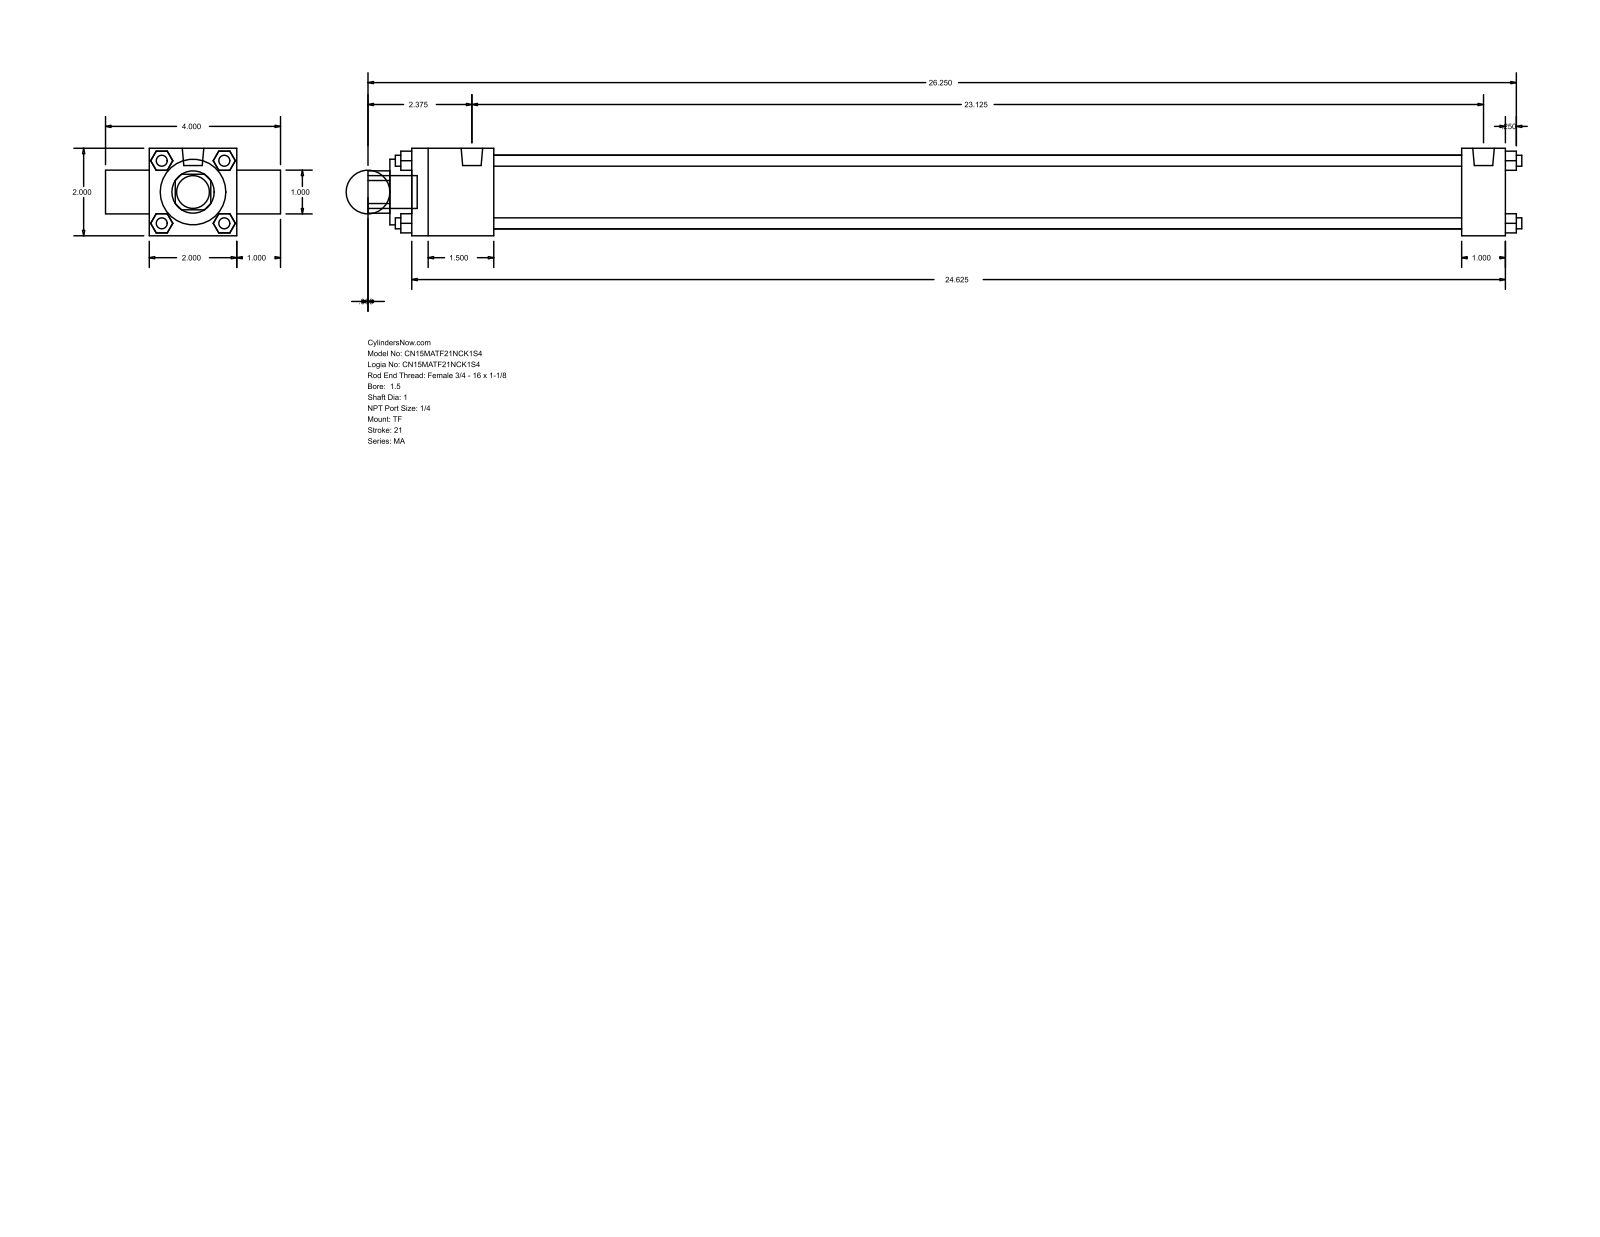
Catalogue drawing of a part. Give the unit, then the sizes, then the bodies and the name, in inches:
Units: inches
Overall size (bounding box): 26.375 × 4 × 2
Round holes (diameter × count): ⌀1 ×2, ⌀1.5 ×1, ⌀1.69 ×1
Round bosses / shafts (diameter × count): ⌀0.25 ×4, ⌀0.313 ×3, ⌀0.492 ×2, ⌀0.75 ×1
Partial cylindrical surfaces — rounded edges, fillets, slot ends (radius × count): R0.484 ×1
Main face-to-face distances: 2, 1, 25, 3, 0.25, 1.875, 24, 22.125, 23.125, 25.5
Bodies: 0 solids, 120 faces (92 planar, 28 cylindrical, 0 other)
Part name (STEP PRODUCT): MA_TF__0150_1
STEP written by: GSSL Pune (CONFIG_CONTROL_DESIGN)
